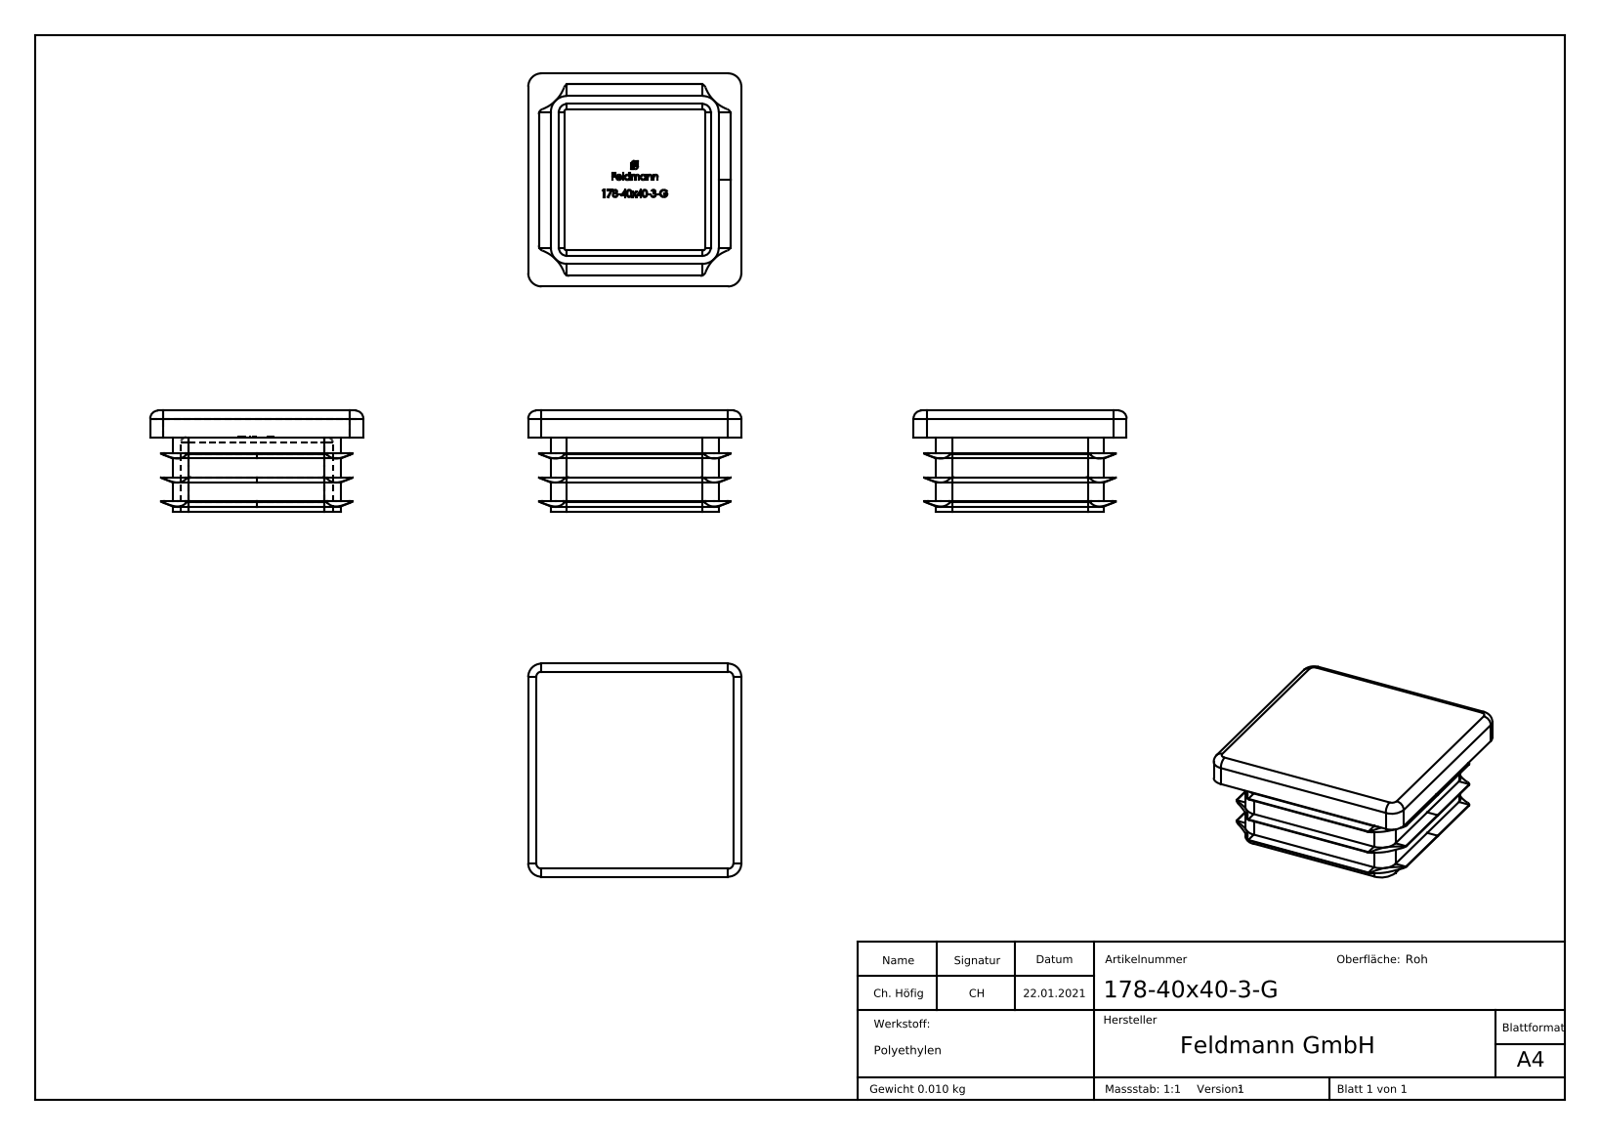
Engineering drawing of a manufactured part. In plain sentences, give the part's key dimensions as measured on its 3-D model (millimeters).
The part is named "178-40x40-3-G". Its 3-D file was written by "SolidWorks 2018 (CONFIG_CONTROL_DESIGN)". It is 1 solid with 497 faces: 256 planar, 83 cylindrical and 158 other. Overall it measures 40 by 40 by 19 millimeters. Its volume is 10 765 cubic millimeters and its surface area 8 319 square millimeters. Partial cylindrical surfaces (rounded edges, fillets, slot ends): 12 of radius 1, 8 of radius 1.5, 4 of radius 2.5, 4 of radius 3, 4 of radius 7. The main face-to-face distances are 5, 1.5, 30, 28.5, 31.5, 4.25, 5.75, 34.25, 35.75, 4.17.
